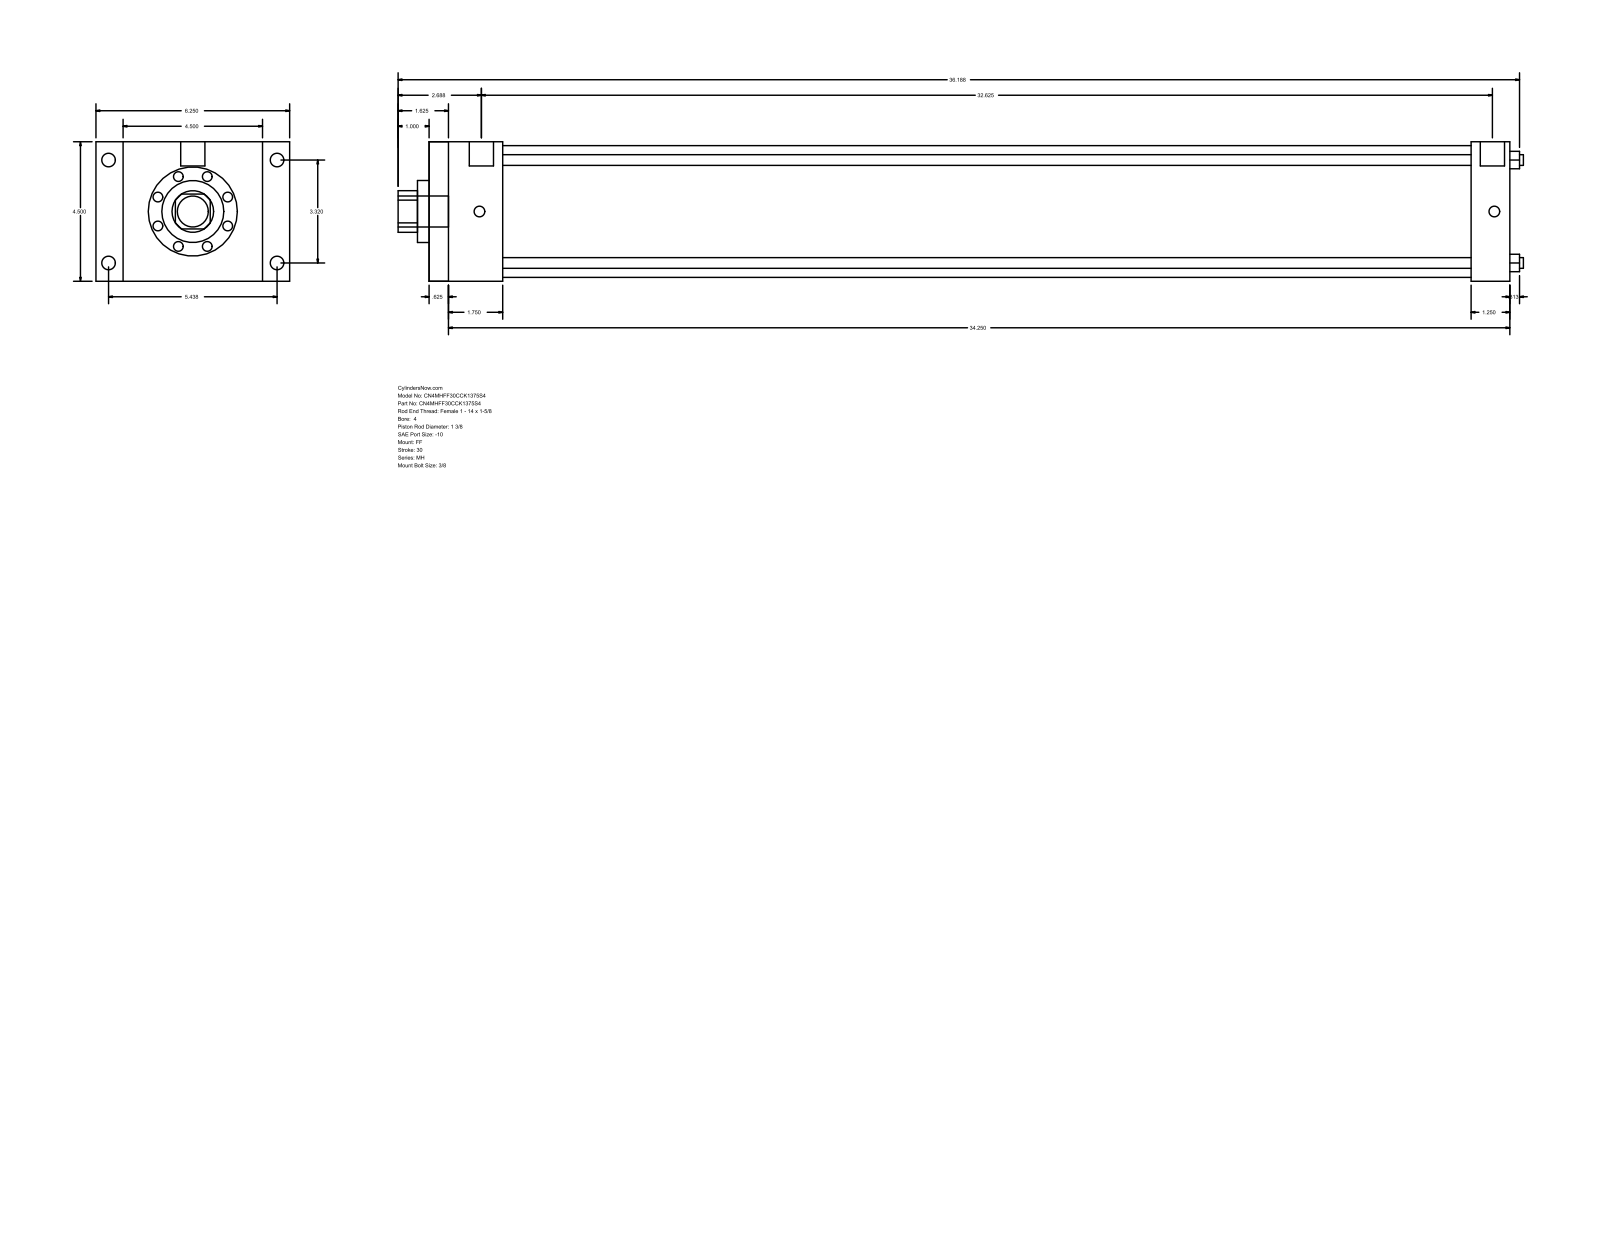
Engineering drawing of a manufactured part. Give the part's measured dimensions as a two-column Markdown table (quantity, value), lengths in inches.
| quantity | value |
| --- | --- |
| part name | MH_FF__0400_1.375 |
| STEP written by | GSSL Pune (CONFIG_CONTROL_DESIGN) |
| units | inches |
| bodies | 0 solids, 92 faces (64 planar, 28 cylindrical, 0 other) |
| overall size | 36.313 × 6.25 × 4.5 |
| round holes (diameter × count) | 0.345 × 4, 1.375 × 1, 2 × 1, 4.25 × 1 |
| round bosses / shafts (diameter × count) | 0.438 × 4, 0.344 × 4, 0.781 × 2, 1 × 1 |
| partial cylindrical surfaces (radius × count) | 0.672 × 1 |
| main face-to-face distances | 4.5, 34.875, 0.625, 34.25, 2.375, 1.75, 32.5, 33.625, 33, 31.25 |
| hole center spacings | 2.347, 3.32, 4.695 |
